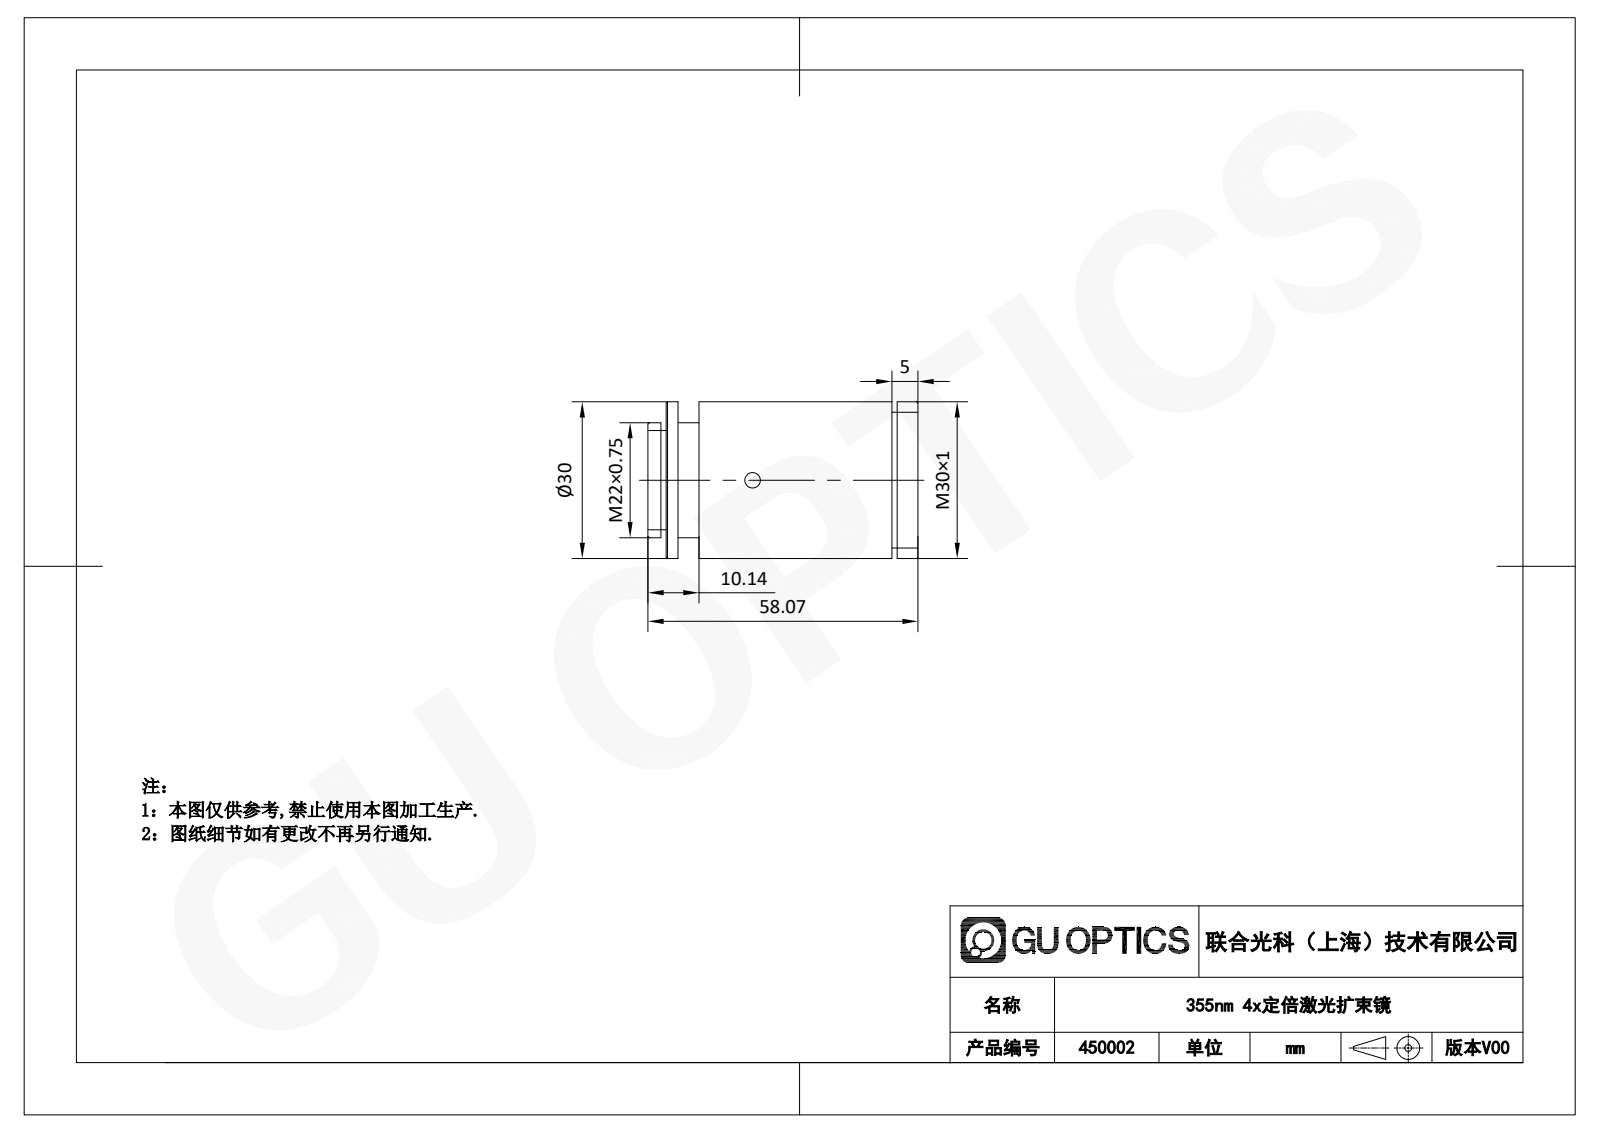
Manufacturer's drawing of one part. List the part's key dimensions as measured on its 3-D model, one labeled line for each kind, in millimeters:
Part name (STEP PRODUCT): 450002
STEP written by: SolidWorks 2020 (AUTOMOTIVE_DESIGN)
Units: millimetres
Bodies: 1 solid, 43 faces (11 planar, 22 cylindrical, 10 other)
Overall size (bounding box): 58.07 × 30 × 30
Volume: 31 175 mm³ · Surface area: 10 459 mm²
Round holes (diameter × count): ⌀8 ×1, ⌀18 ×1
Round bosses / shafts (diameter × count): ⌀30 ×1, ⌀26 ×1, ⌀22 ×1, ⌀19 ×1
Main face-to-face distances: 4, 47.93, 50.57, 54.57, 2.64, 51.93, 6.64, 43.93, 3.5, 6.14
